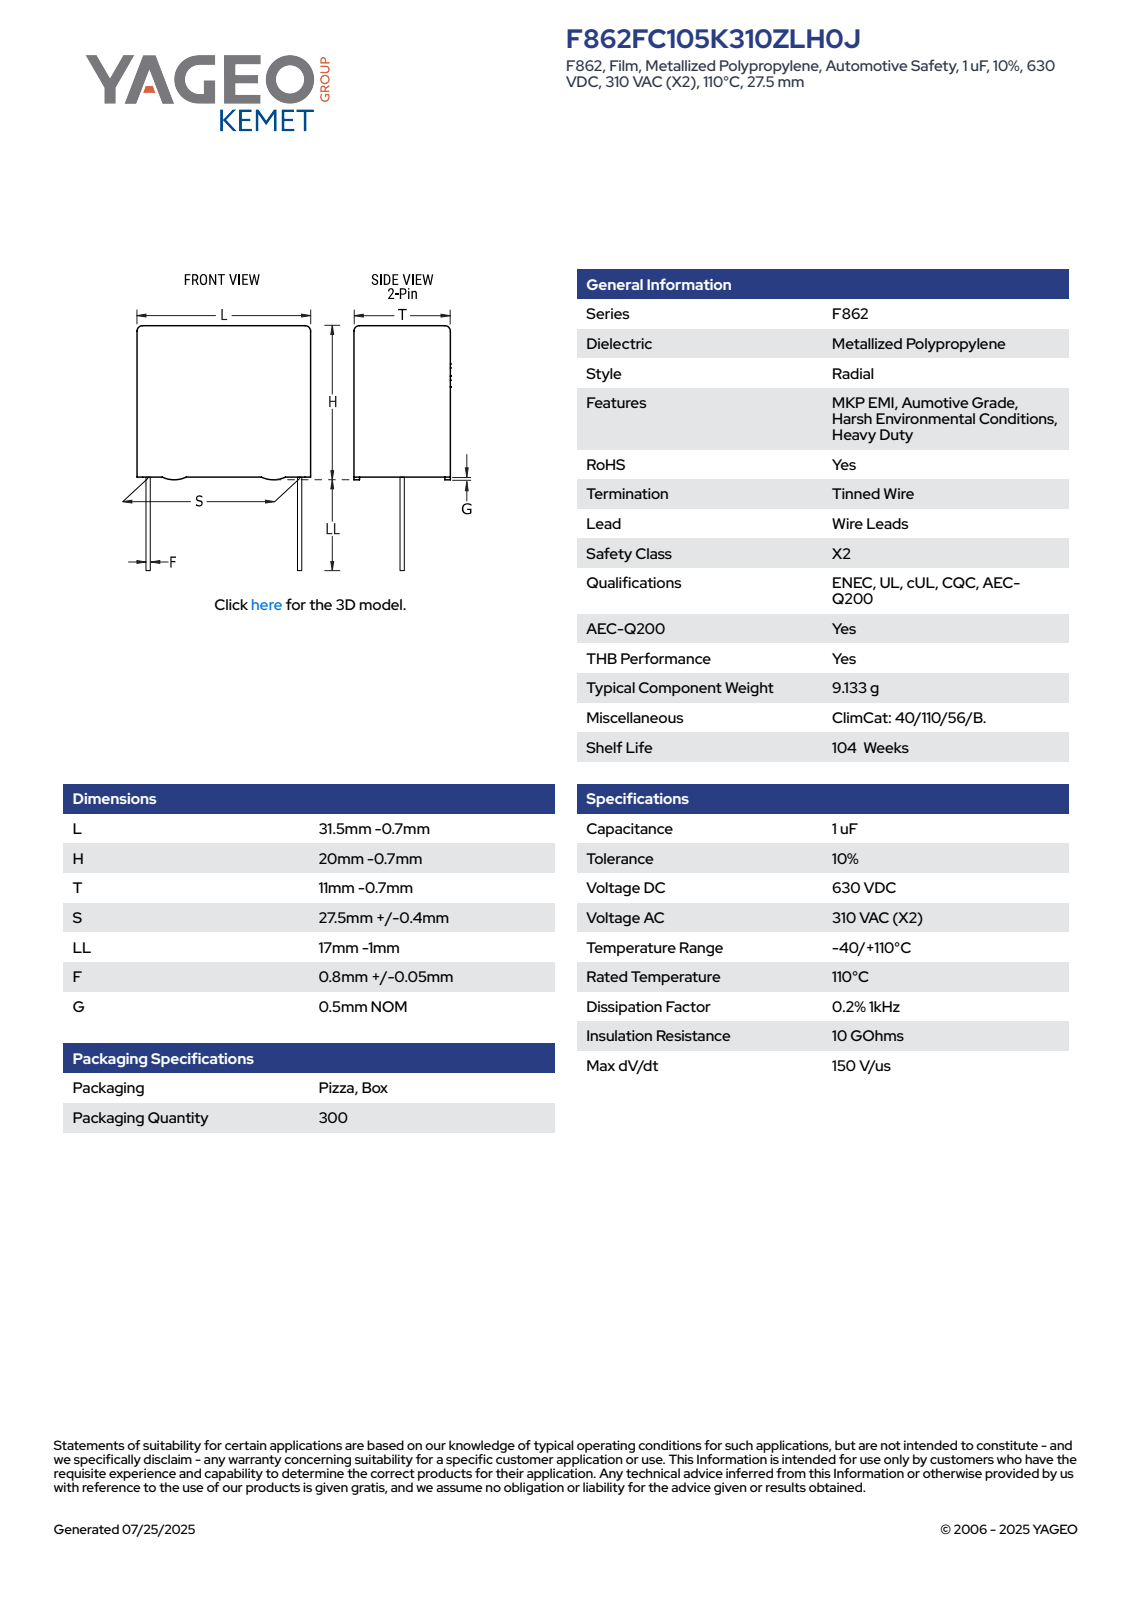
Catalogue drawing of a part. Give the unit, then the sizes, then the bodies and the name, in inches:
Units: inches
Overall size (bounding box): 1.39 × 1.213 × 0.406
Round bosses / shafts (diameter × count): ⌀0.033 ×2
Partial cylindrical surfaces — rounded edges, fillets, slot ends (radius × count): R0.02 ×4
Main face-to-face distances: 0.406, 0.74, 1.213, 0.02, 0.76, 0.023, 0.382, 0.359, 0.63, 0.65
Volume: 0.365 in³ · Surface area: 3.68 in²
Bodies: 4 solids, 89 faces (81 planar, 8 cylindrical, 0 other)
Part name (STEP PRODUCT): CFR_RBG_31.5X20X11_L30.8H19.3T10.3S27.5LL16F0.85G0.5
STEP written by: SolidWorks 2014 (AUTOMOTIVE_DESIGN)
